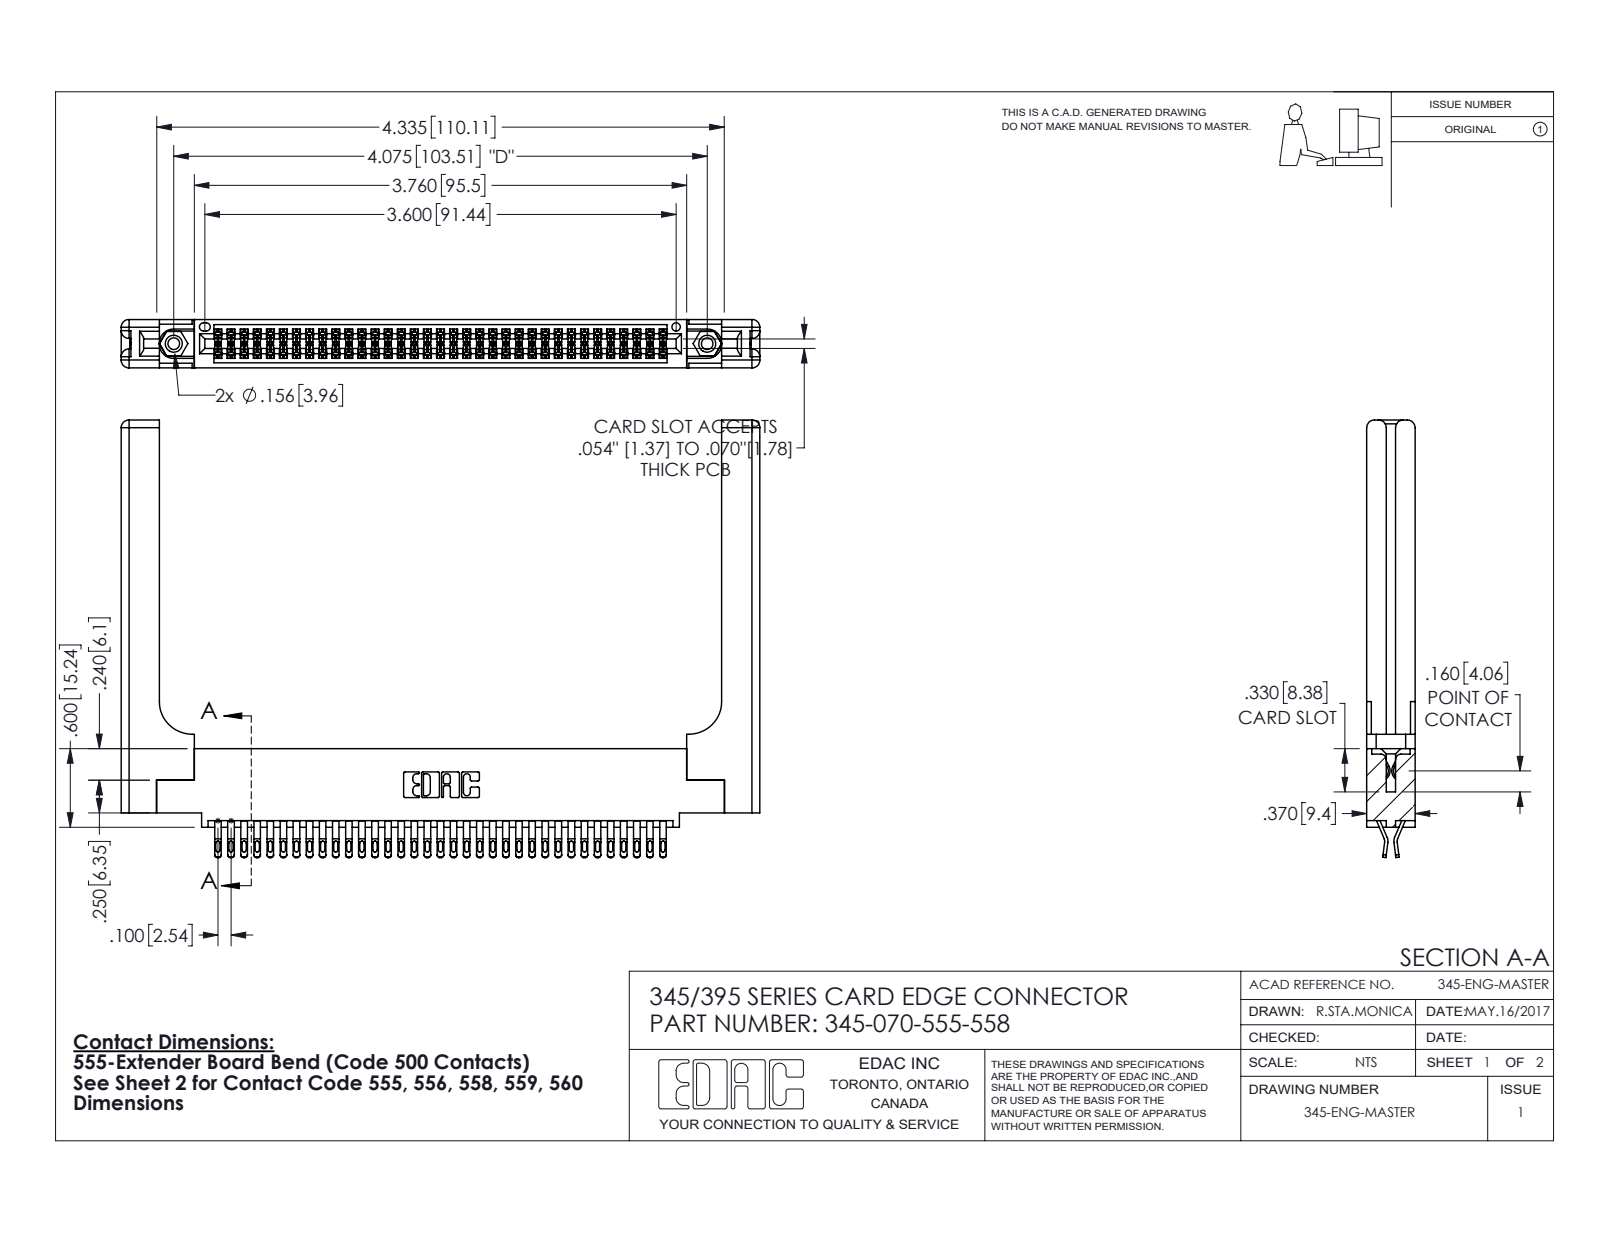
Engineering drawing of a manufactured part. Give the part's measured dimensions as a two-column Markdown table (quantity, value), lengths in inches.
| quantity | value |
| --- | --- |
| part name | 345-250-001_345-250-001-102; 345-292-001_555 Tail; 345-220-058_345-220-058; 345 Part_0.110 Offset - 0.156 Dia-TH (+1 more) |
| STEP written by | SolidWorks 2016 (CONFIG_CONTROL_DESIGN) |
| units | inches |
| bodies | 75 solids, 4306 faces (2402 planar, 1844 cylindrical, 60 other) |
| overall size | 4.879 × 3.342 × 0.37 |
| volume | 1.256 in³ |
| surface area | 36.6 in² |
| round holes (diameter × count) | 0.089 × 2, 0.125 × 2, 0.156 × 2, 0.064 × 1 |
| round bosses / shafts (diameter × count) | 0.155 × 2 |
| partial cylindrical surfaces (radius × count) | 0.016 × 175, 0.02 × 140, 0.006 × 105, 0.01 × 22, 0.06 × 16, 0.007 × 6, 0.031 × 6, 0.026 × 3 |
| main face-to-face distances | 0.37, 0.072, 0.298, 0.025, 0.098, 0.272, 0.2, 0.225, 0.148, 0.15 |
| hole center spacings | 0.27, 3.839, 4.075 |
